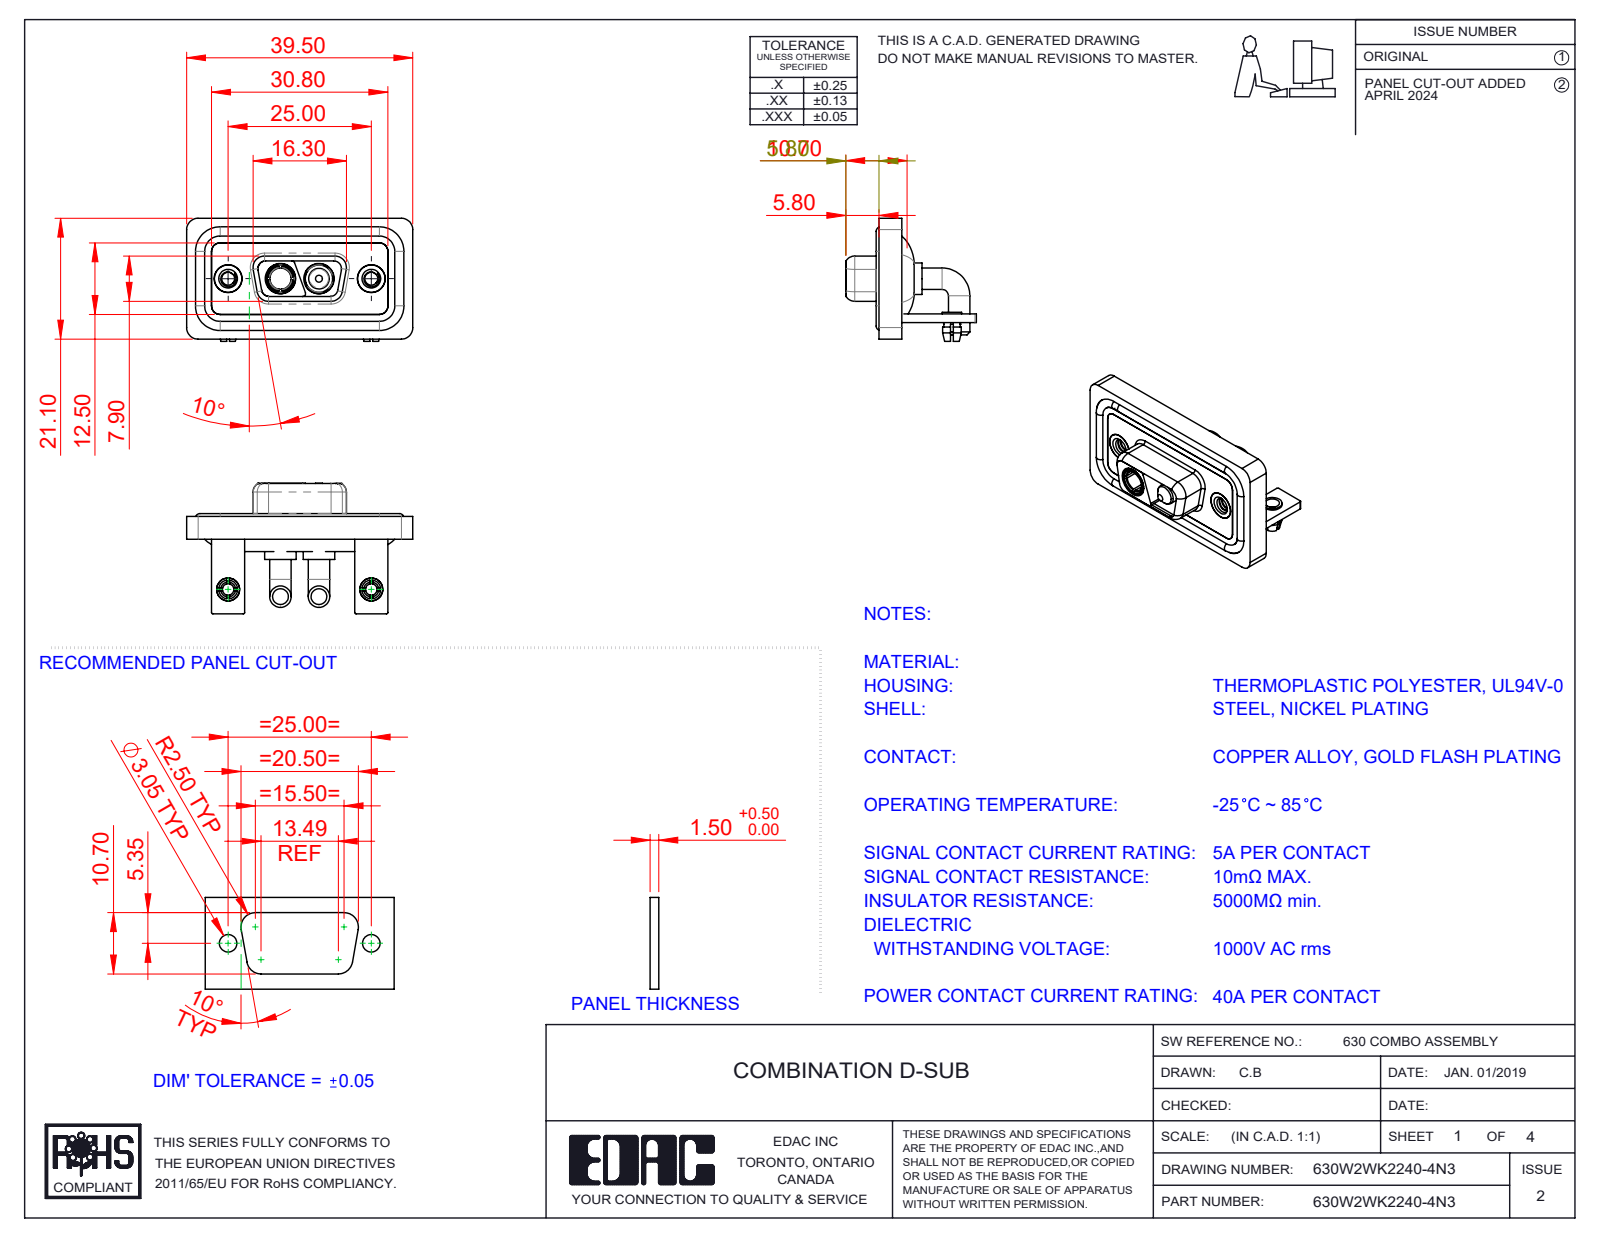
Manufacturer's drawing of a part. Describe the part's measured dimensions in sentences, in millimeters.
The part is named "Power Pin_40A RA; 630Combo Housing_2WK2; 630Combo Stabilizer Bracket_50 Contacts; 630Combo Threaded Rivet_2 (+6 more)". Its 3-D file was written by "SolidWorks 2023 (CONFIG_CONTROL_DESIGN)". It is 15 solids with 648 faces: 212 planar, 291 cylindrical and 145 other. Overall it measures 39.5 by 22.8 by 21.5 millimeters. Its volume is 5 255 cubic millimeters and its surface area 8 528 square millimeters. Round holes: 4 of diameter 4.85, 2 of diameter 2, 2 of diameter 2.26, 2 of diameter 2.5, 2 of diameter 3.2, 2 of diameter 4, 2 of diameter 4.05, 2 of diameter 5, 2 of diameter 5.3, 1 of diameter 3.7. Round bosses or shafts: 4 of diameter 3.75, 4 of diameter 1.6, 2 of diameter 5.5, 2 of diameter 5.2, 2 of diameter 4.95, 2 of diameter 4.8, 2 of diameter 4.75, 2 of diameter 4. Partial cylindrical surfaces (rounded edges, fillets, slot ends): 19 of radius 2, 18 of radius 1.5, 16 of radius 0.25, 8 of radius 1.35, 8 of radius 1.6, 7 of radius 0.5, 4 of radius 0.6, 4 of radius 0.65. The main face-to-face distances are 0.4, 2.9, 1.5, 1.1, 3.7, 1.8, 0.8, 2.5, 1.6, 3.1. The hole center spacings are 9.14, 15.86, 25, 6.72.
